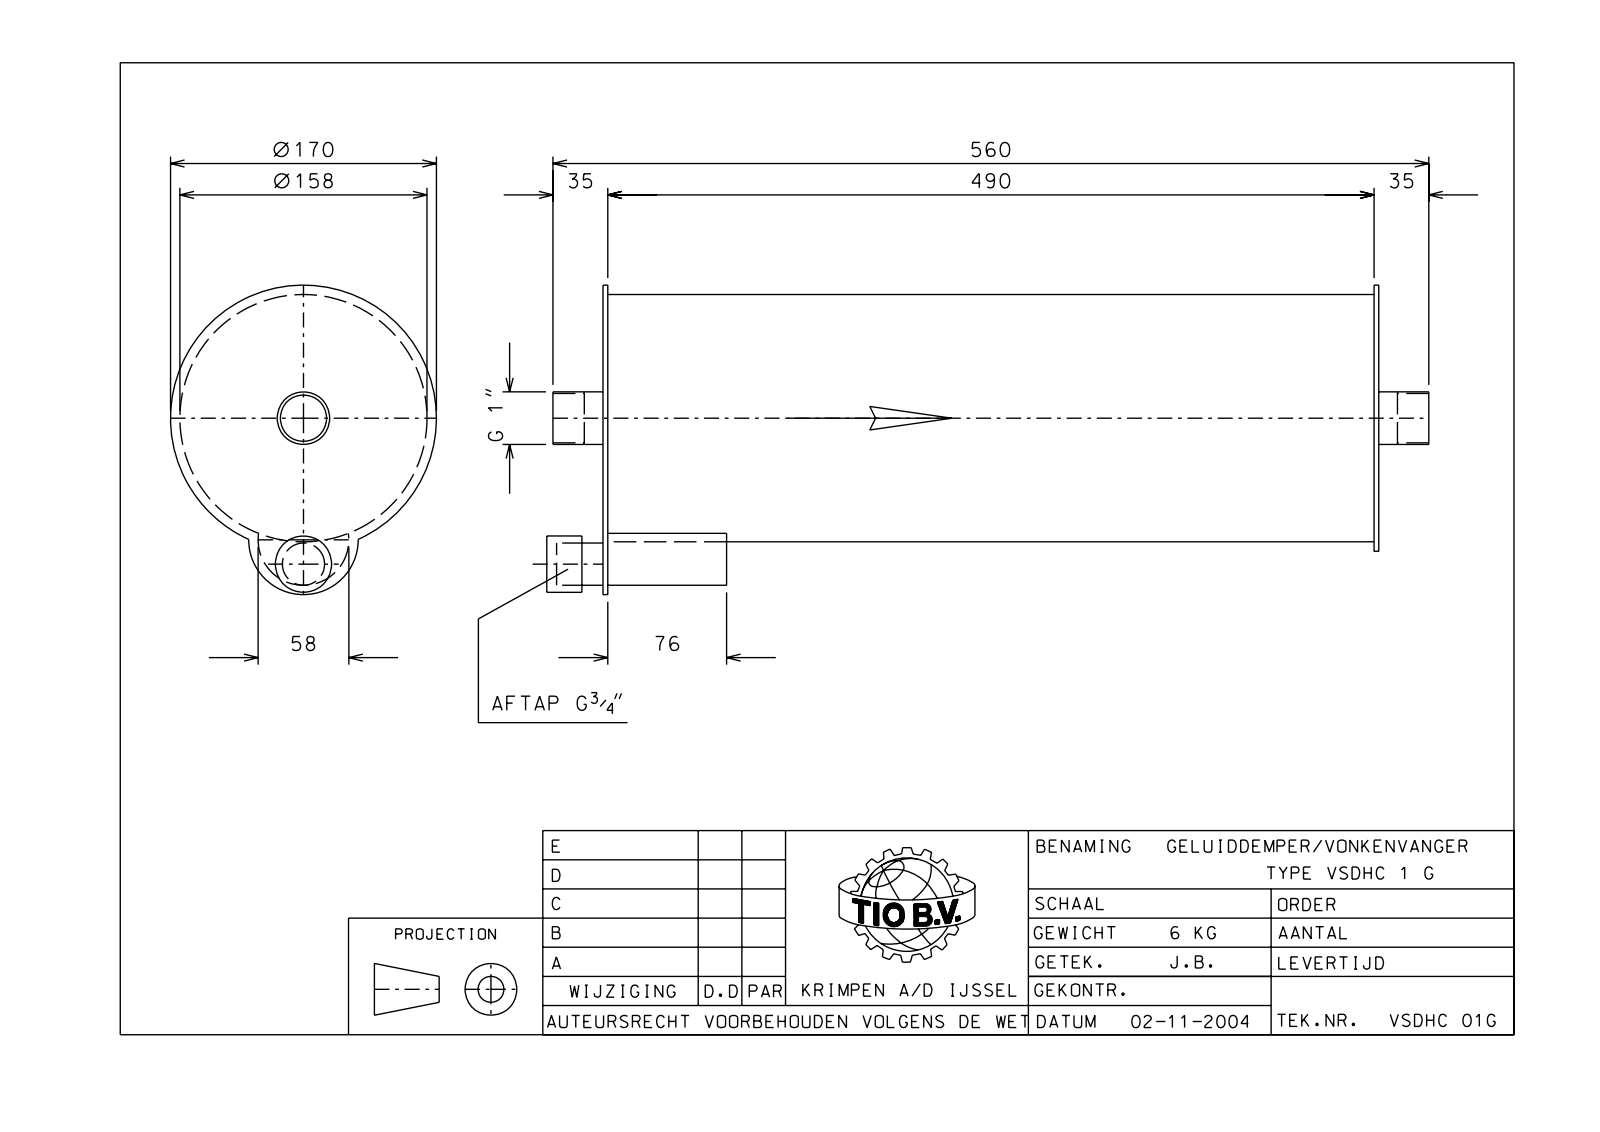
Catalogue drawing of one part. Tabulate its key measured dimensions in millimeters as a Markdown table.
| quantity | value |
| --- | --- |
| part name | MAAT3D |
| STEP written by | Autodesk Inventor 2015 (AUTOMOTIVE_DESIGN) |
| units | millimeters |
| bodies | 9 solids, 56 faces (32 planar, 24 cylindrical, 0 other) |
| overall size | 571 × 194.5 × 170 |
| volume | 554 364 mm³ |
| surface area | 626 517 mm² |
| round holes (diameter × count) | 21 × 1, 29 × 1, 31 × 1, 35.6 × 1, 155 × 1, 158 × 1 |
| round bosses / shafts (diameter × count) | 170 × 1, 35 × 1, 33.6 × 1, 30.6 × 1, 26 × 1 |
| partial cylindrical surfaces (radius × count) | 27.5 × 1, 29 × 1, 35 × 1 |
| main face-to-face distances | 3, 493, 490, 496, 79, 414, 76, 417, 21, 100 |
| hole center spacings | 91 |
